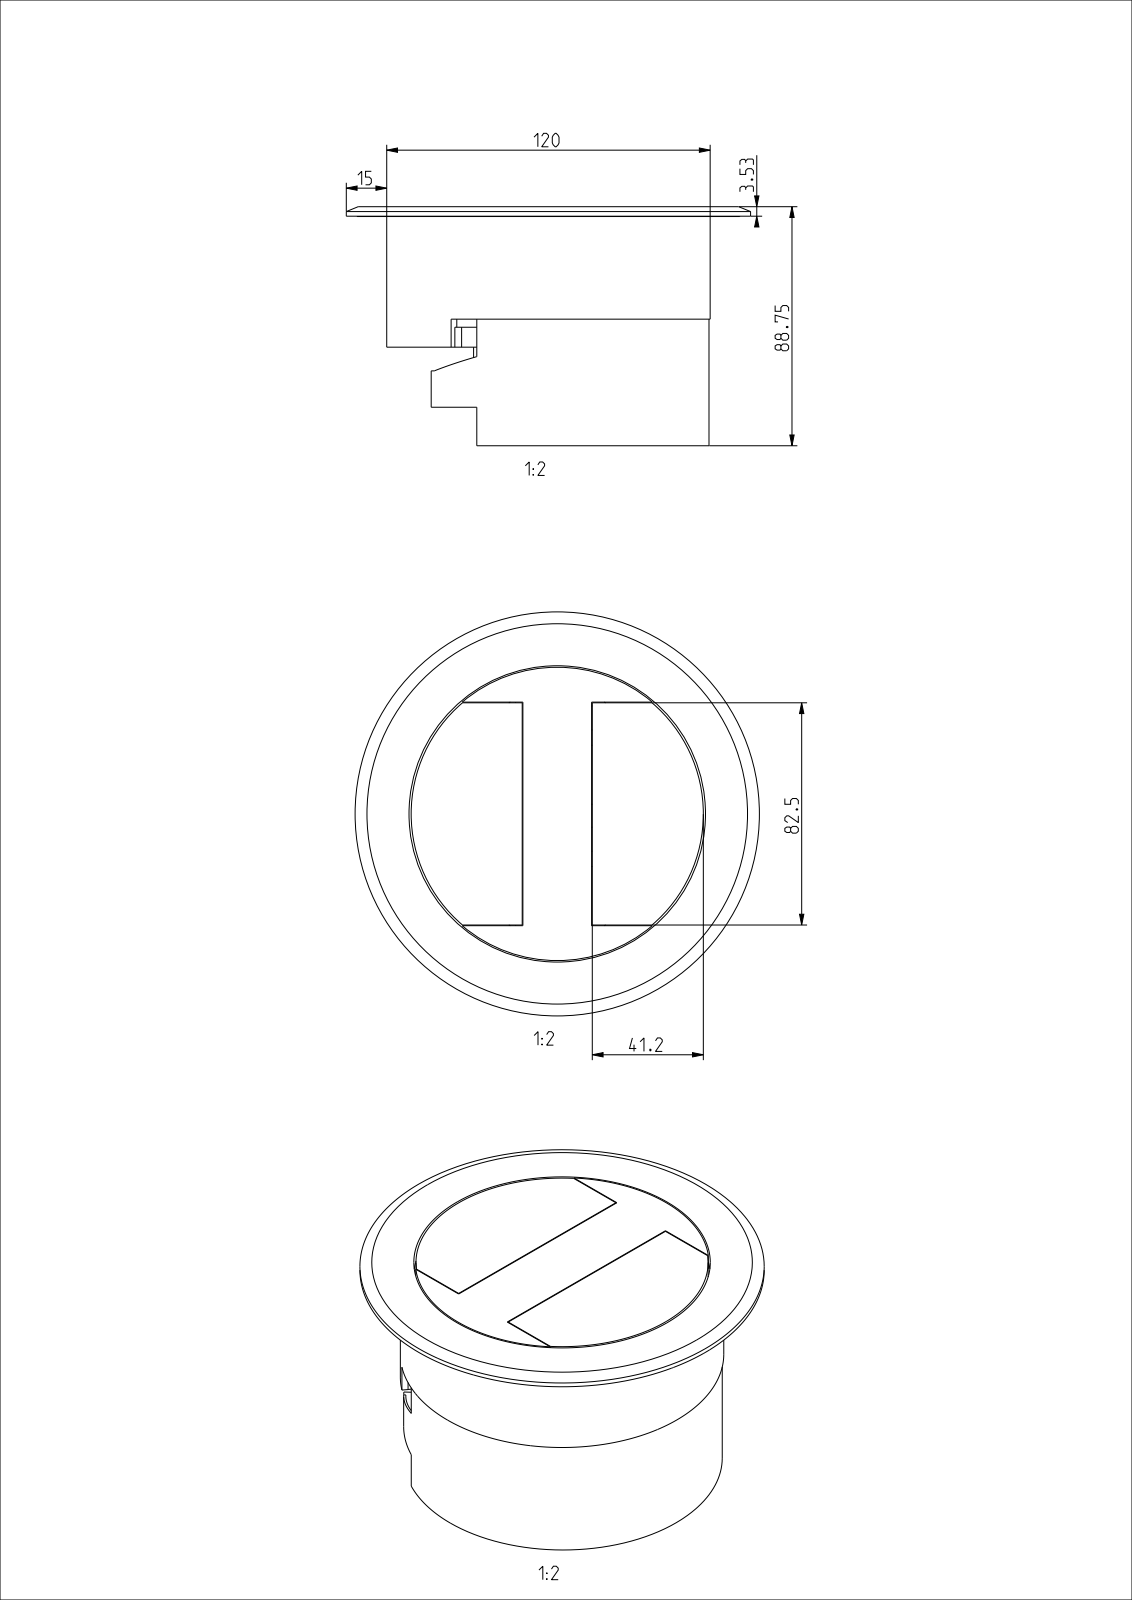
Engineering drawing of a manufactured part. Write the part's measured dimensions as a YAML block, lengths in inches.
part_name: "BSR_BECHERUNTERTEIL; BSR_BECHEROBERTEIL; BSR_GERTEAUFNAHME0; BSM012KUN (+3 more)"
step_written_by: "CREO PARAMETRIC BY PTC INC, 2022024 (AUTOMOTIVE_DESIGN)"
units: inches
bodies: {solids: 6, faces: 334, planar: 271, cylindrical: 61, other: 2}
overall_size: [5.906, 5.906, 3.494]
volume: 20.72
surface_area: 317.4
round_holes:
  - {diameter: 0.224, count: 4}
  - {diameter: 0.107, count: 2}
  - {diameter: 1.508, count: 2}
  - {diameter: 0.079, count: 1}
  - {diameter: 0.142, count: 1}
  - {diameter: 3.543, count: 1}
  - {diameter: 4.331, count: 1}
  - {diameter: 4.543, count: 1}
  - {diameter: 5.685, count: 1}
round_bosses_or_shafts:
  - {diameter: 0.185, count: 2}
  - {diameter: 5.906, count: 1}
  - {diameter: 5.591, count: 1}
  - {diameter: 4.724, count: 1}
  - {diameter: 4.528, count: 1}
partial_cylinders:
  - {radius: 1.969, count: 2}
  - {radius: 2.008, count: 1}
  - {radius: 2.047, count: 1}
  - {radius: 2.087, count: 1}
  - {radius: 2.134, count: 1}
  - {radius: 2.144, count: 1}
  - {radius: 2.144, count: 1}
  - {radius: 2.165, count: 1}
face_to_face_distances: [0.059, 0.089, 1.441, 3.346, 1.5, 3.406, 3.494, 3.435, 1.906, 1.994]
hole_center_spacings: [0.348, 1.772, 0.696, 1.698, 0.623, 0.833, 0.903, 0.954]
